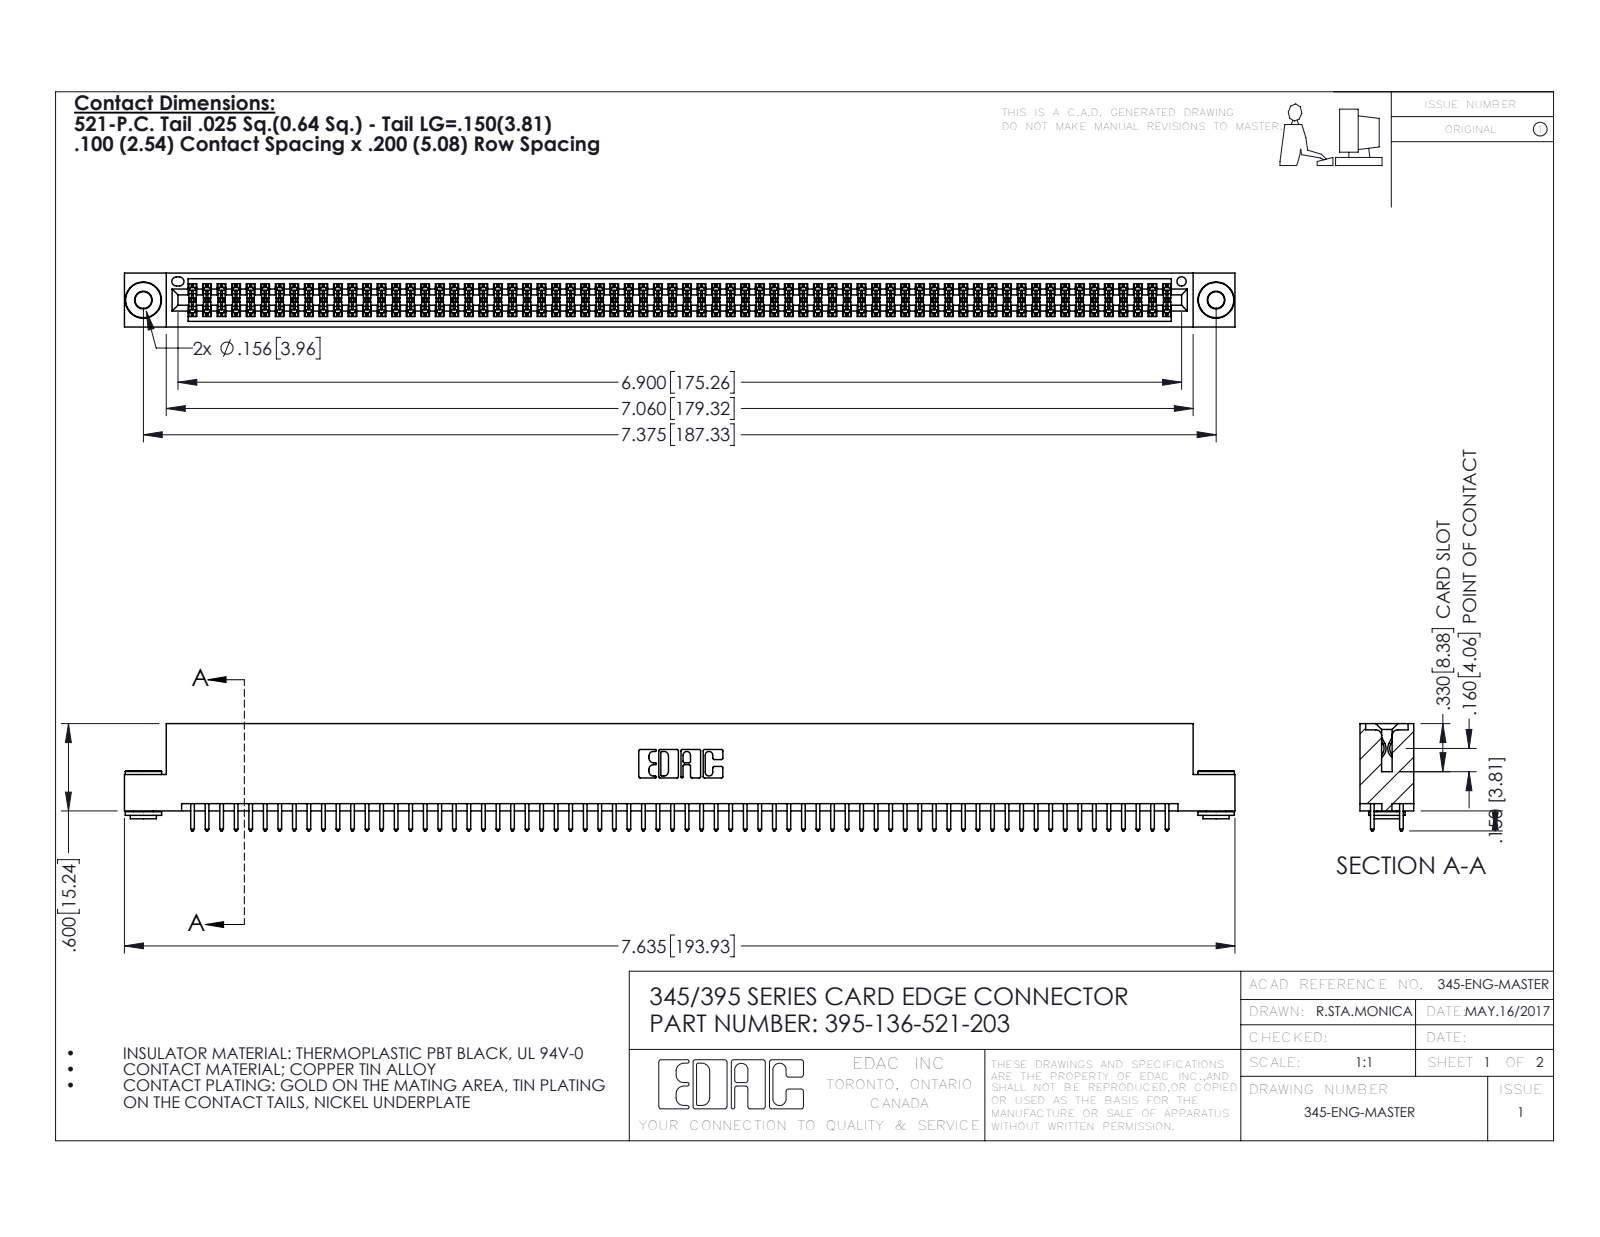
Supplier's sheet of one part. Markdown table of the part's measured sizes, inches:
| quantity | value |
| --- | --- |
| part name | 345-250-002_345-250-002-102; 395-136-521-203; 345 Part_Flush Mounting Lugs - 0.156 Dia-TH; 345-292-001_345-293-121 |
| STEP written by | SolidWorks 2016 (CONFIG_CONTROL_DESIGN) |
| units | inches |
| bodies | 139 solids, 6964 faces (4578 planar, 2378 cylindrical, 8 other) |
| overall size | 7.635 × 0.737 × 0.37 |
| volume | 1.162 in³ |
| surface area | 44.17 in² |
| round holes (diameter × count) | 0.116 × 2, 0.156 × 2, 0.064 × 1 |
| round bosses / shafts (diameter × count) | 0.25 × 2, 0.18 × 2, 0.136 × 2 |
| partial cylindrical surfaces (radius × count) | 0.006 × 204, 0.01 × 136, 0.01 × 22, 0.007 × 6, 0.031 × 6, 0.026 × 3, 0.014 × 2, 0.019 × 2 |
| main face-to-face distances | 0.072, 0.298, 0.2, 0.025, 0.098, 0.272, 0.37, 0.225, 0.175, 0.149 |
| hole center spacings | 0.27, 7.139, 7.375 |
